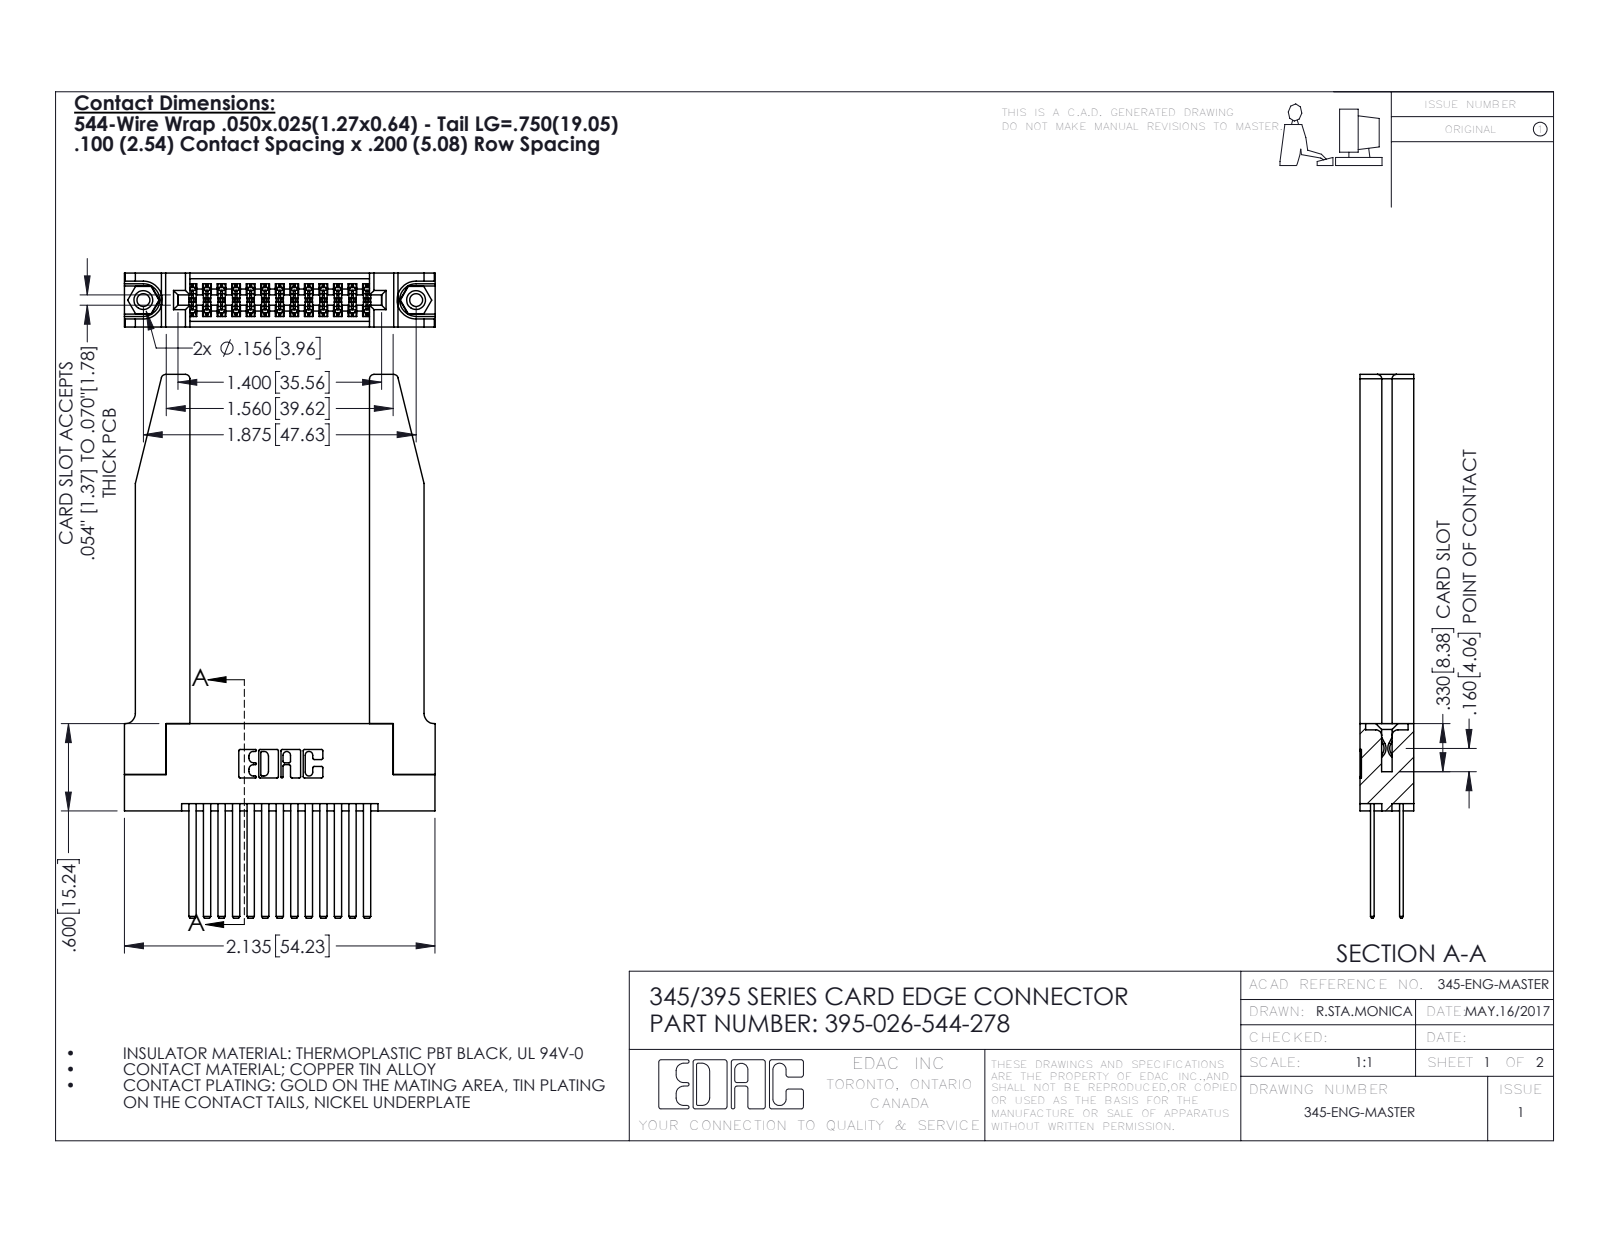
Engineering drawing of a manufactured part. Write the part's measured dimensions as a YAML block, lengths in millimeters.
part_name: "395-026-544-278; 345-220-078_345-220-078; 345 Part_Flush Mounting Lugs - 0.156 Dia-TH; 345-292-001_345-293-144 (+1 more)"
step_written_by: "SolidWorks 2016 (CONFIG_CONTROL_DESIGN)"
units: millimeters
bodies: {solids: 31, faces: 1504, planar: 976, cylindrical: 476, other: 52}
overall_size: [94.9, 54.3, 9.4]
volume: 13100
surface_area: 15280
round_holes:
  - {diameter: 2.3, count: 2}
  - {diameter: 3.2, count: 2}
  - {diameter: 4, count: 2}
  - {diameter: 1.6, count: 1}
round_bosses_or_shafts:
  - {diameter: 3.9, count: 2}
partial_cylinders:
  - {radius: 0.2, count: 39}
  - {radius: 0.3, count: 22}
  - {radius: 0.8, count: 8}
  - {radius: 0.2, count: 6}
  - {radius: 0.8, count: 6}
  - {radius: 0.7, count: 3}
  - {radius: 0.4, count: 2}
  - {radius: 0.5, count: 2}
face_to_face_distances: [9.4, 1.8, 7.6, 5.1, 2.5, 6.9, 0.6, 5.7, 3.8, 3.8]
hole_center_spacings: [6.9, 41.7, 47.6]
